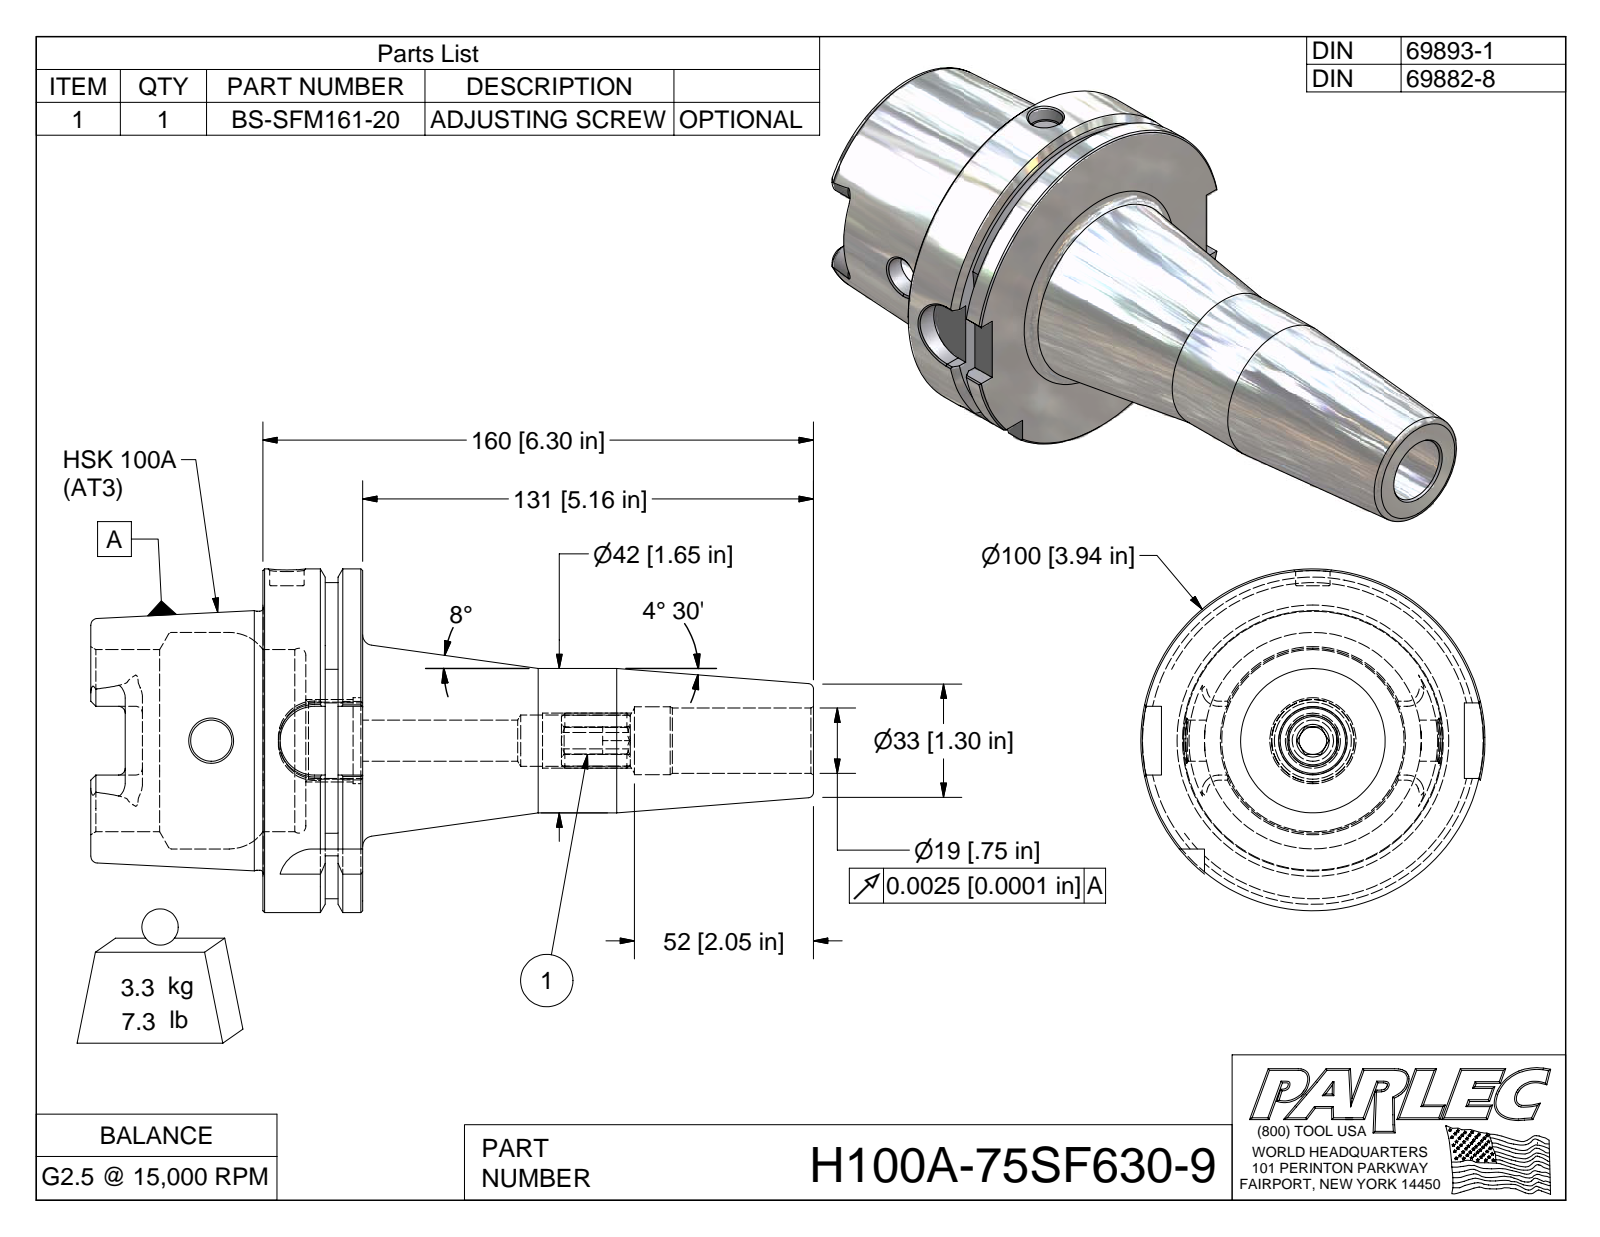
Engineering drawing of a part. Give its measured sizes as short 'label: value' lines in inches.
name: H100A-75SF630-9; H100A-75SF630-9-1; BS-SFM161-20
written by: Autodesk Inventor 2009 (AUTOMOTIVE_DESIGN)
unit: in
bodies: 2 solids, 151 faces (50 planar, 30 cylindrical, 71 other)
size: 8.269 × 3.937 × 3.937
volume: 25.83 in³; area: 114.8 in²
holes: 1× ⌀0.394, 1× ⌀0.472, 1× ⌀0.749, 1× ⌀0.779, 1× ⌀0.881, 1× ⌀0.985, 1× ⌀2.087, 1× ⌀2.48
bosses: 1× ⌀3.937, 1× ⌀2.967, 1× ⌀1.654
rounds: 4× R0.394, 3× R0.079, 2× R0.192, 1× R0.315, 1× R1.811
face distances: 1.142, 0.492, 0.65, 1.969, 2.461, 3.11, 2.682, 0.713, 0.221, 0.428
